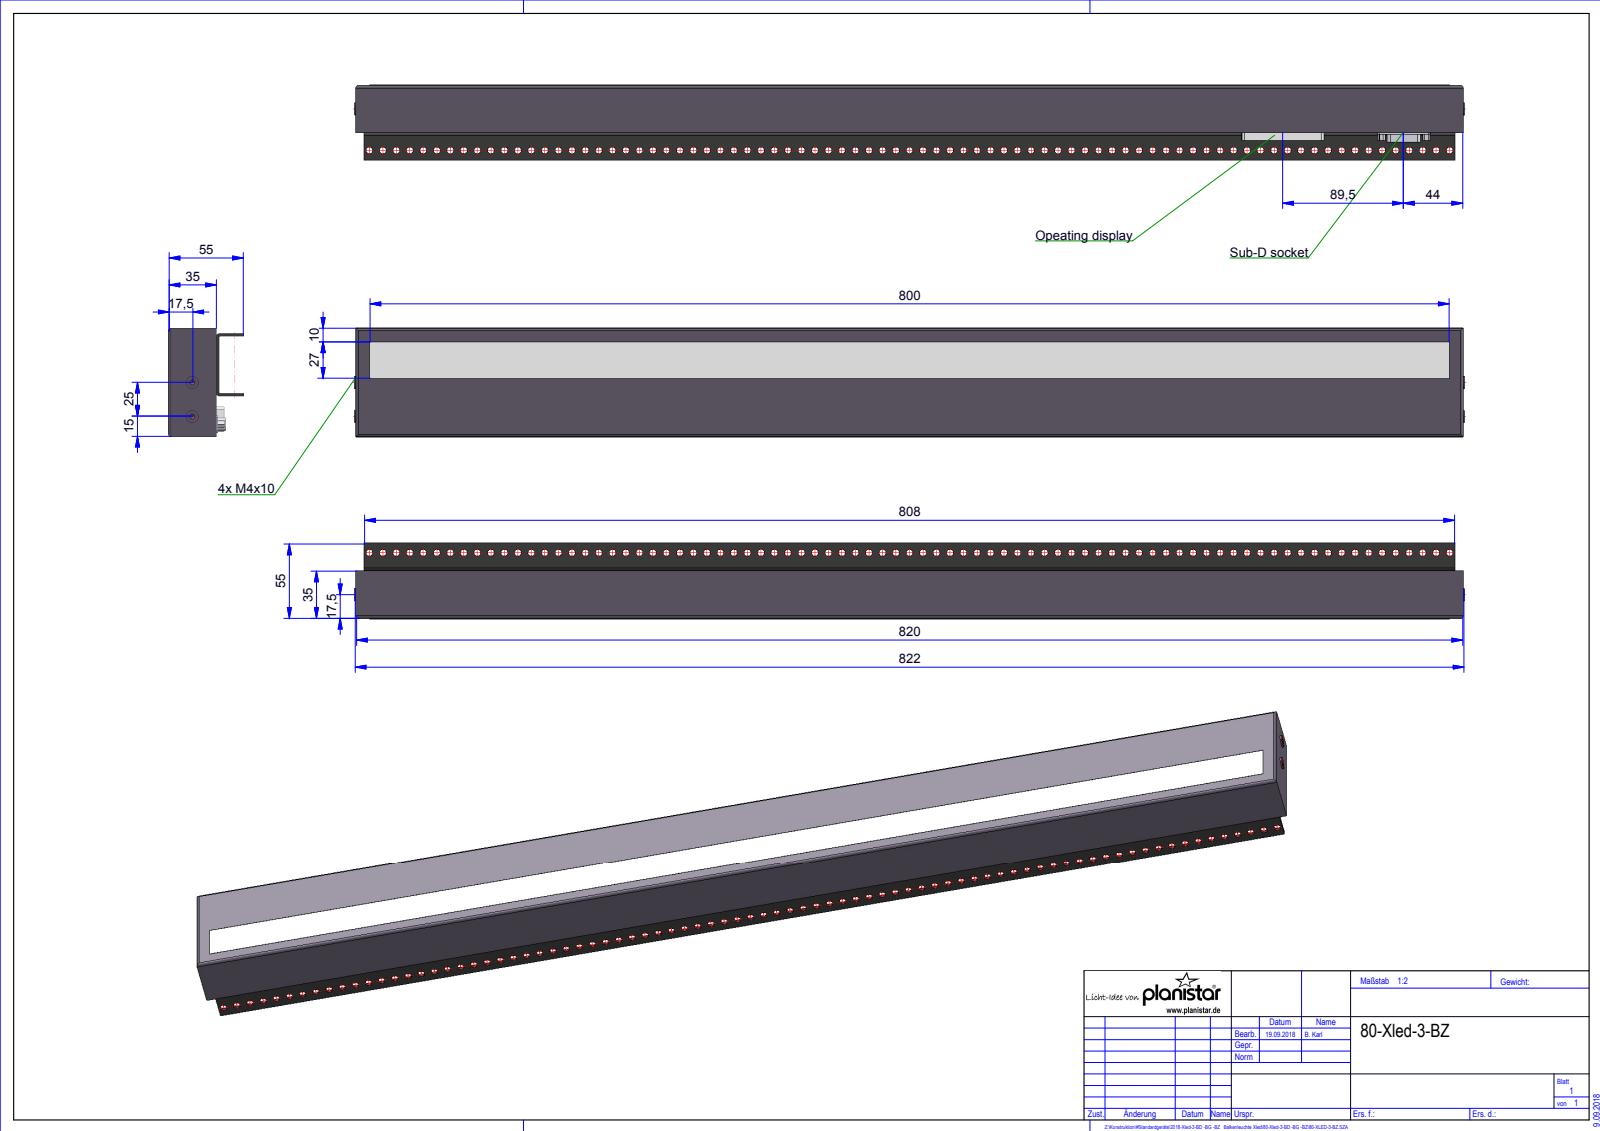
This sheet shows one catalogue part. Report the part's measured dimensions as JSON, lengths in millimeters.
{"part_name": "Root; Baugruppe_Xled-2-VD; QUADER_0; Baugruppe_Baugruppe (+5 more)", "step_written_by": "HiCAD 2015 2002.1 Build 408 (AUTOMOTIVE_DESIGN)", "units": "millimeters", "bodies": {"solids": 13, "faces": 323, "planar": 86, "cylindrical": 224, "other": 13}, "overall_size": [822, 80, 55.1], "volume_mm3": 2428000, "surface_area_mm2": 331770, "round_holes": [[5, 81], [2.5, 2], [3, 2], [3.3, 2], [4, 2]], "round_bosses_or_shafts": [[1, 5], [8, 3], [9, 2], [3.6, 2]], "partial_cylinders_radius": [[0.2, 12], [2, 10], [1.5, 4], [2.1, 4], [2.5, 4], [1, 2]], "face_to_face_distances": [2, 35, 37, 80, 44, 35.1, 37.1, 4, 76, 30], "hole_center_spacings": [10, 20, 30, 40, 50, 60, 70, 80]}
